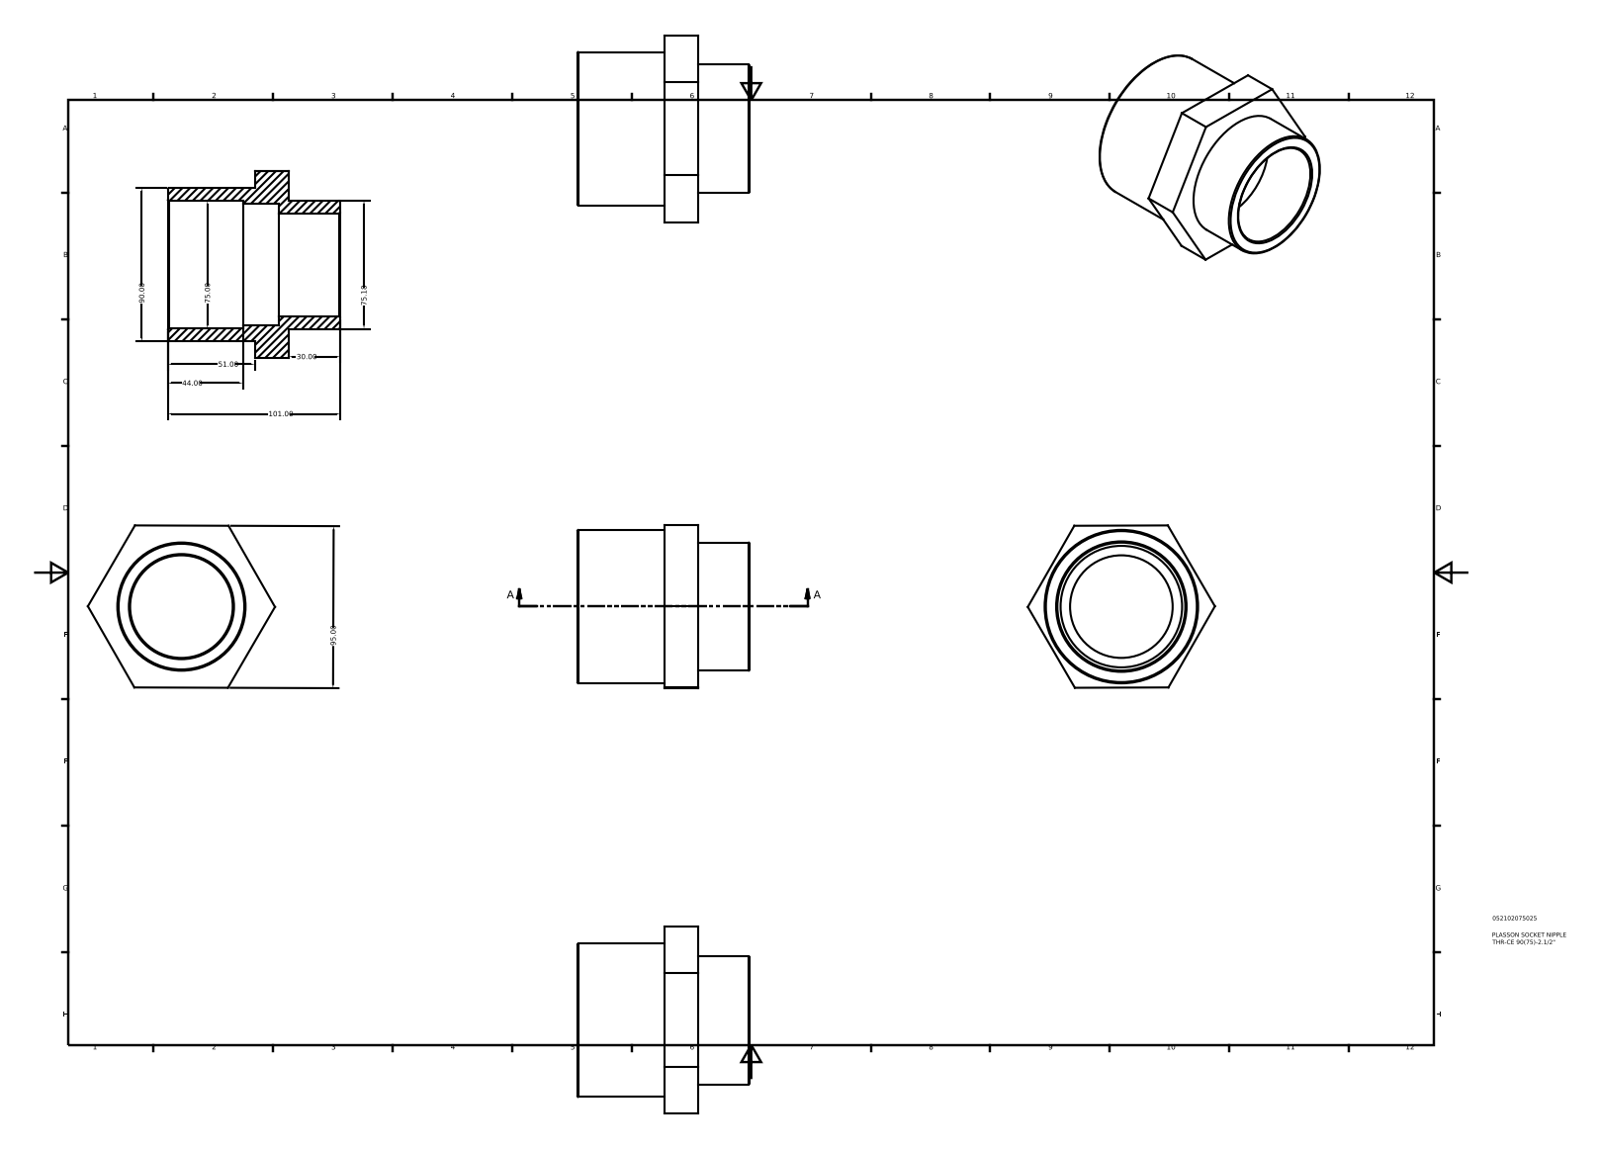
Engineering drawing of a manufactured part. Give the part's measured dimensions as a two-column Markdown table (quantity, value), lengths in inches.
| quantity | value |
| --- | --- |
| part name | 052102075025 |
| STEP written by | Autodesk Inventor 2015 (AUTOMOTIVE_DESIGN) |
| units | inches |
| bodies | 1 solid, 21 faces (12 planar, 5 cylindrical, 4 other) |
| overall size | 4.319 × 3.976 × 3.748 |
| volume | 14.25 in³ |
| surface area | 92.38 in² |
| round holes (diameter × count) | 2.368 × 1, 2.805 × 1, 2.953 × 1 |
| round bosses / shafts (diameter × count) | 3.543 × 1, 2.96 × 1 |
| main face-to-face distances | 2.795, 2.008, 0.787, 3.976, 1.969, 1.181, 2.559, 0.551, 0.236, 1.417 |
